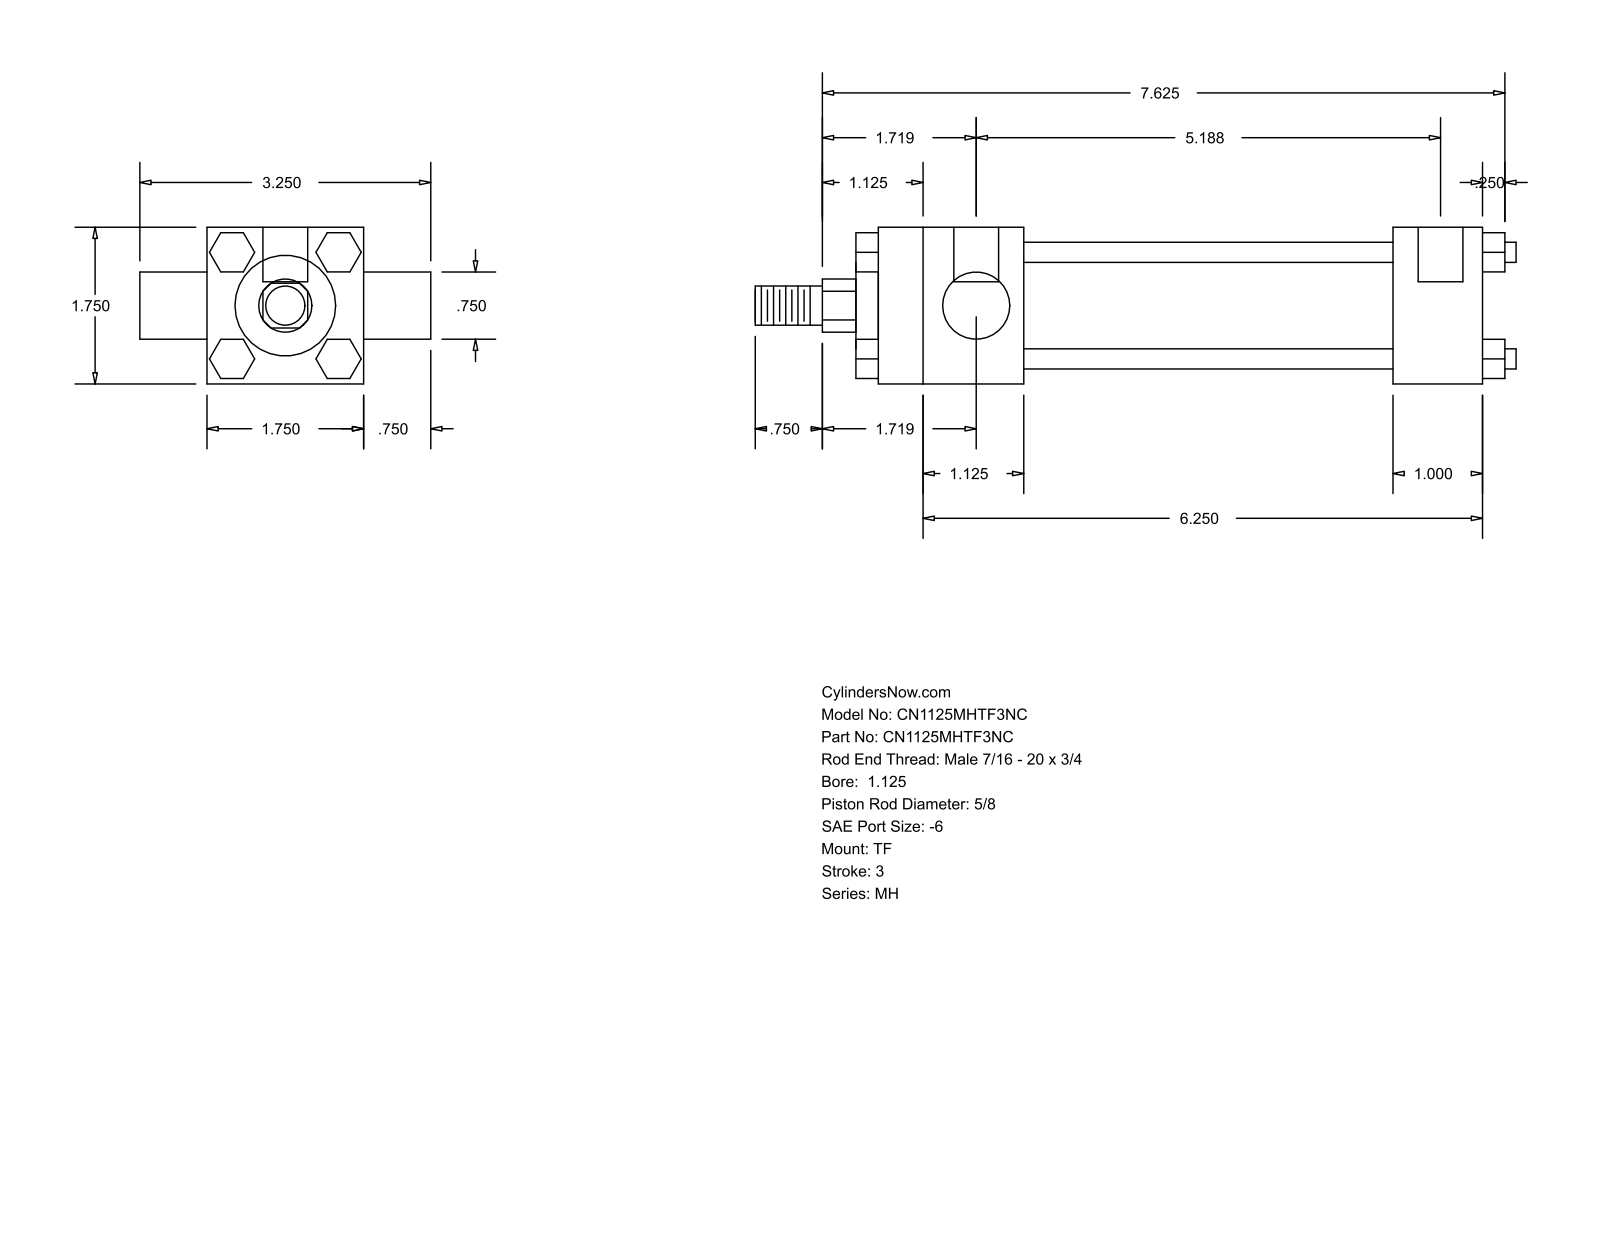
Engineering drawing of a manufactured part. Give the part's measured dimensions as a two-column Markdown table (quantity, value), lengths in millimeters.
| quantity | value |
| --- | --- |
| part name | MH_TF__0112_0.625 |
| STEP written by | GSSL Pune (CONFIG_CONTROL_DESIGN) |
| units | millimeters |
| bodies | 0 solids, 120 faces (92 planar, 28 cylindrical, 0 other) |
| overall size | 215.9 × 82.55 × 44.45 |
| round holes (diameter × count) | 5.56 × 3, 12.7 × 2 |
| round bosses / shafts (diameter × count) | 5.71 × 4, 34.92 × 1, 28.57 × 1, 19.05 × 1, 15.88 × 1, 11.11 × 1 |
| partial cylindrical surfaces (radius × count) | 7.54 × 1 |
| main face-to-face distances | 44.46, 11.11, 104.78, 130.17, 25.39, 41.27, 146.05, 171.44, 47.62, 6.35 |
| hole center spacings | 3.17, 128.59, 131.76 |
